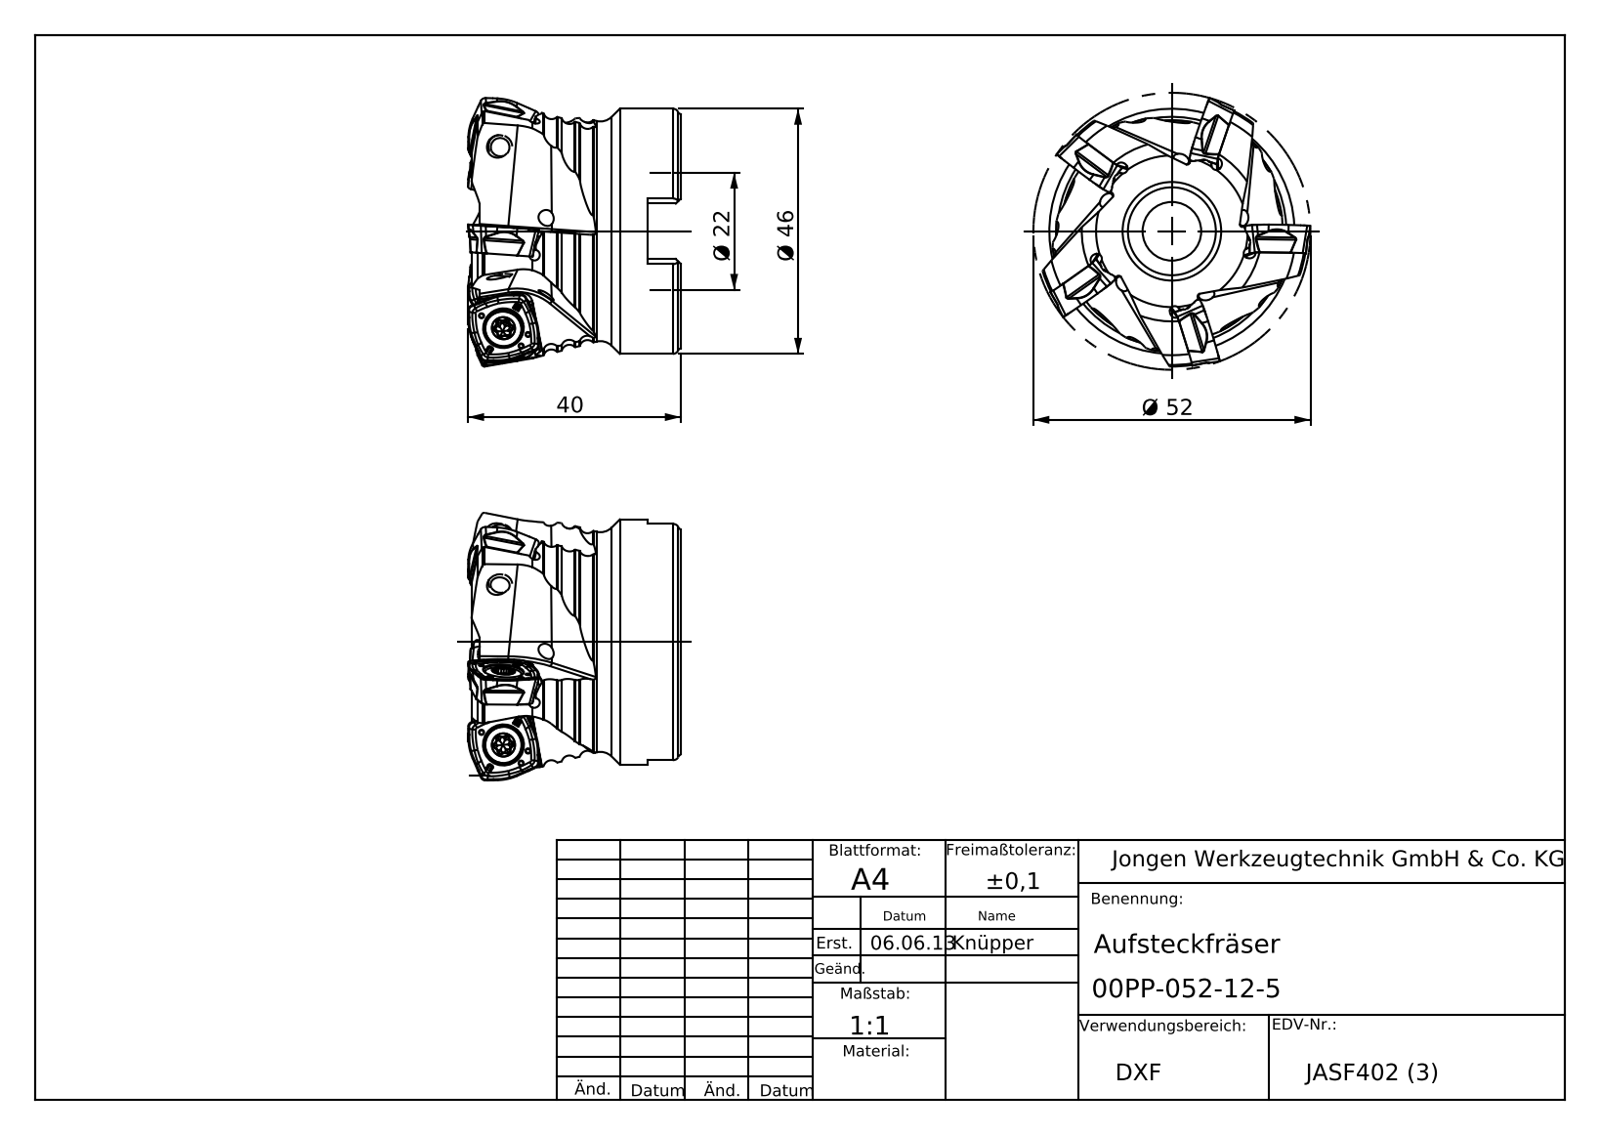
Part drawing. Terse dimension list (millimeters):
name: 00PP-052-12-5
written by: SolidWorks 2013 (AUTOMOTIVE_DESIGN)
unit: mm
bodies: 1 solid, 280 faces (98 planar, 51 cylindrical, 131 other)
size: 51.97 × 51.97 × 39.94
volume: 49 234 mm³; area: 13 267 mm²
holes: 5× ⌀3, 1× ⌀11, 1× ⌀16.5, 1× ⌀22, 1× ⌀22.15, 1× ⌀22.3
bosses: 1× ⌀46
rounds: 10× R0.5, 10× R1.3, 5× R1, 5× R2
face distances: 37.75, 6.3, 31.45, 10.4, 27.3, 21, 10.45, 20, 13.7, 7.3
